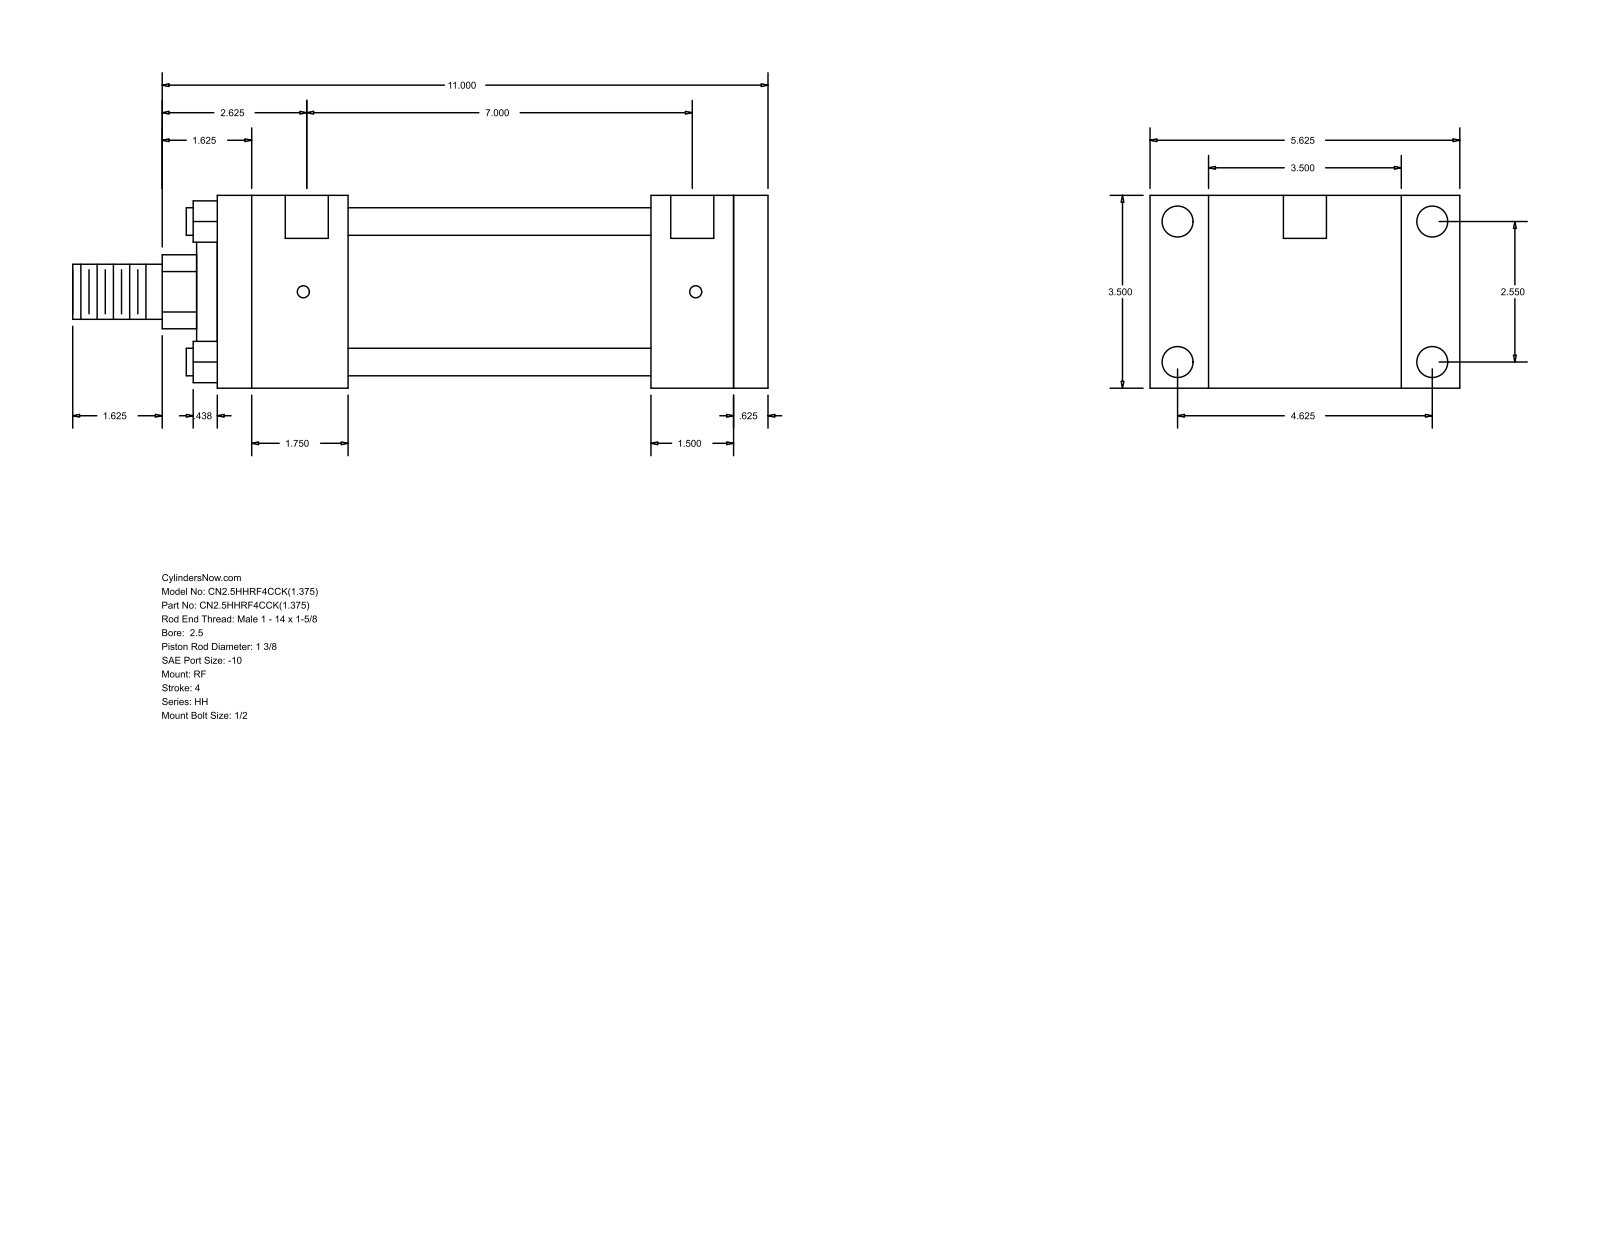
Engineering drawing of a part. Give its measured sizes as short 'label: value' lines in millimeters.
name: HH_RF__0250_1.375
written by: GSSL Pune (CONFIG_CONTROL_DESIGN)
unit: mm
bodies: 0 solids, 92 faces (64 planar, 28 cylindrical, 0 other)
size: 320.68 × 142.88 × 88.9
holes: 4× ⌀5.56, 4× ⌀14.3, 2× ⌀19.84
bosses: 4× ⌀12.7, 1× ⌀73.03, 1× ⌀50.8, 1× ⌀34.92, 1× ⌀25.4
rounds: 1× R17.06
face distances: 88.9, 254, 15.88, 238.12, 53.97, 60.32, 177.8, 193.68, 200.03, 139.71
hole spacings: 64.76, 117.48, 134.15, 180.97, 1.58, 1.59, 177.8, 179.38
